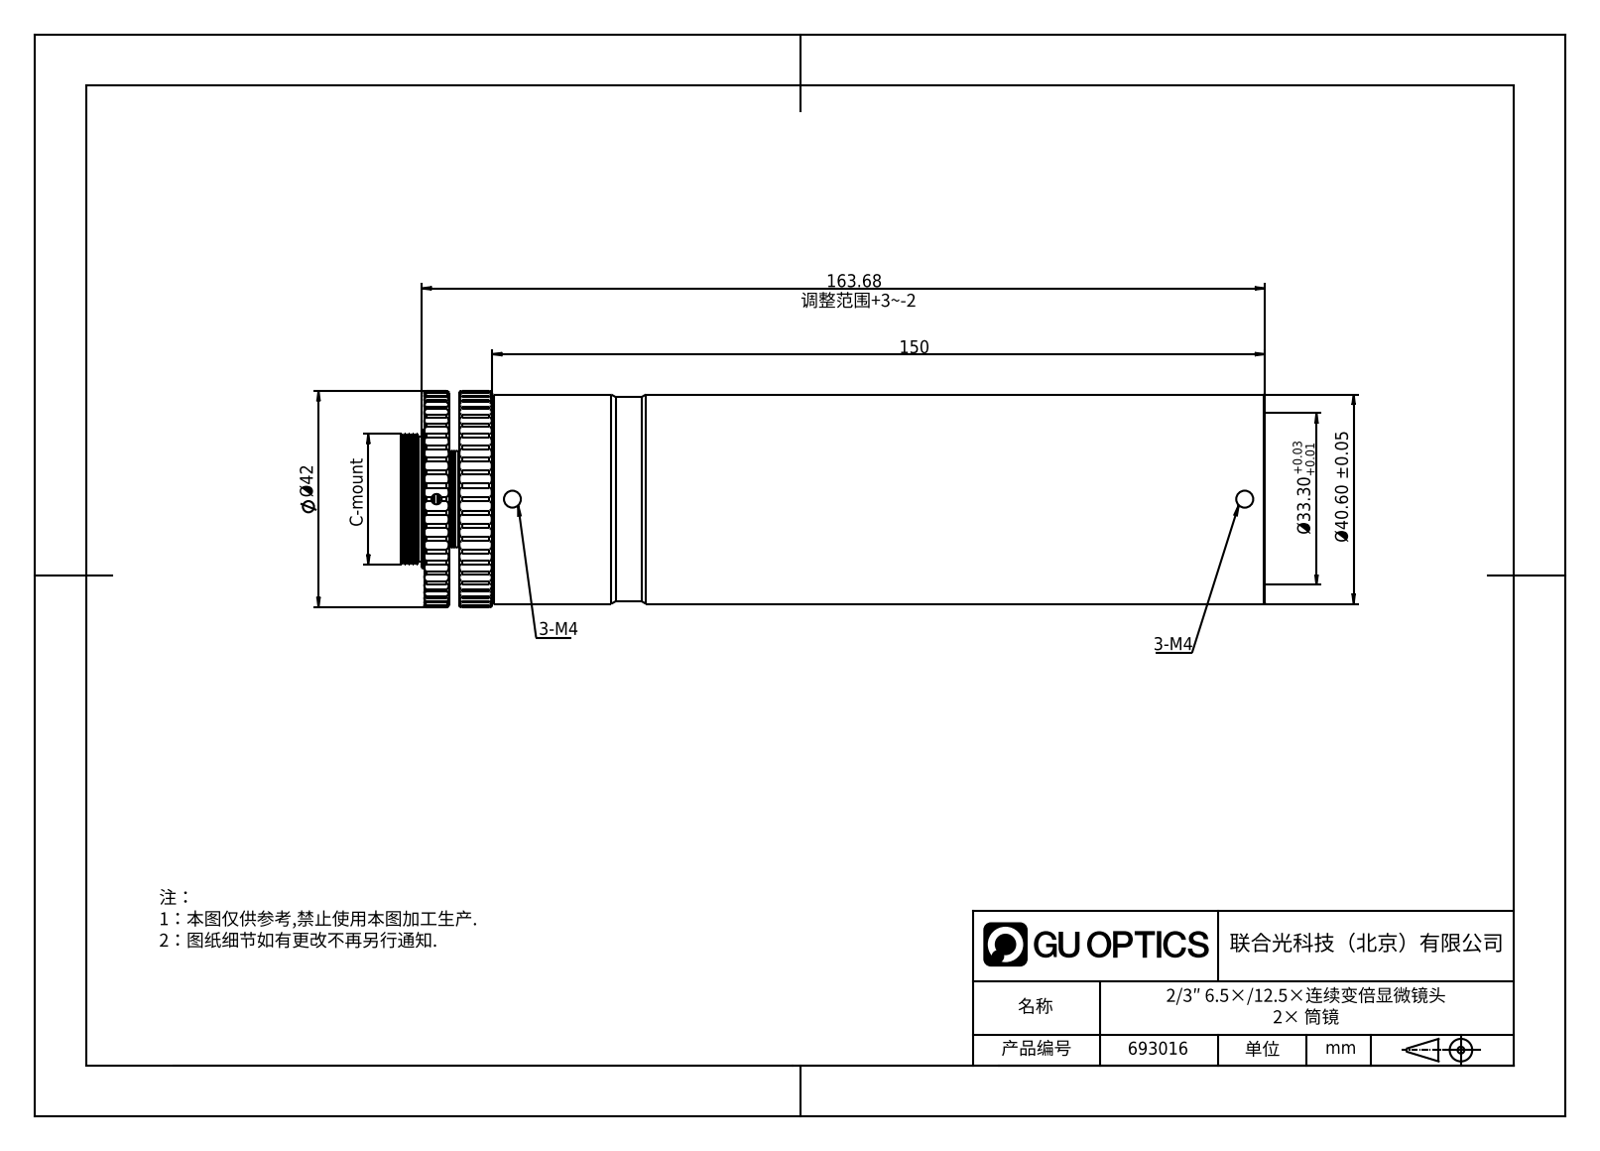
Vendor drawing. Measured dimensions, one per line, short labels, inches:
name: 63020
written by: SolidWorks 2015 (CONFIG_CONTROL_DESIGN)
unit: in
bodies: 0 solids, 331 faces (33 planar, 226 cylindrical, 72 other)
size: 6.602 × 1.654 × 1.652
holes: 6× ⌀0.13, 1× ⌀0.079, 1× ⌀0.098, 1× ⌀1.142, 1× ⌀1.311
bosses: 1× ⌀1.598, 1× ⌀1.559, 1× ⌀1.232, 1× ⌀1.157, 1× ⌀1.063, 1× ⌀1, 1× ⌀0.961
rounds: 50× R0.059, 1× R0.827
face distances: 0.079, 0.268, 0.189, 0.251, 0.33, 0.519, 5.906, 6.157, 6.235, 6.424
hole spacings: 5.595, 0.58, 6.175
